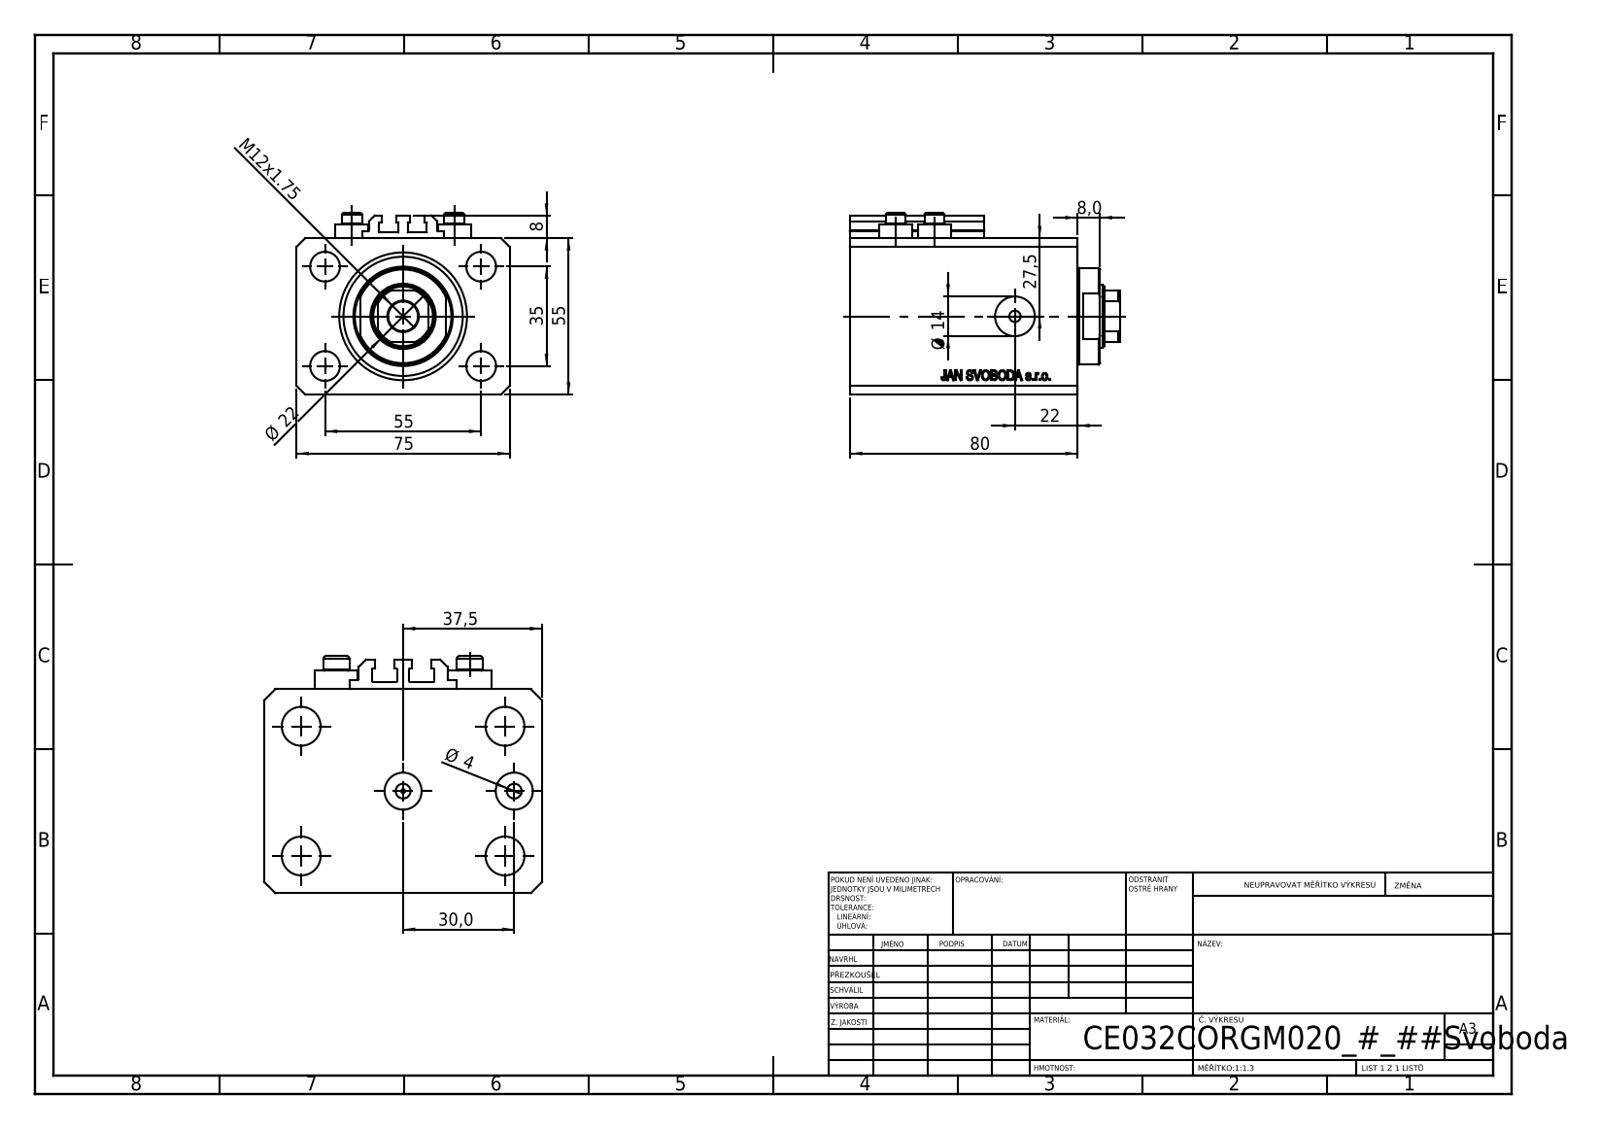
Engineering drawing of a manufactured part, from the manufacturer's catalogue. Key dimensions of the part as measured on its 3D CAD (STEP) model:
Part name (STEP PRODUCT): V250CE_C_VCP; V250CE_C_Body; ALLEN BOLT V250CE; V250CE_VC_C
STEP written by: SolidWorks 2019 (CONFIG_CONTROL_DESIGN)
Units: millimetres
Bodies: 8 solids, 1042 faces (504 planar, 92 cylindrical, 446 other)
Overall size (bounding box): 95 × 75 × 64
Volume: 304 608 mm³ · Surface area: 71 883 mm²
Round holes (diameter × count): ⌀4 ×8, ⌀10.5 ×5, ⌀10 ×2, ⌀14 ×2, ⌀1.25 ×1, ⌀22 ×1, ⌀32 ×1, ⌀45 ×1
Round bosses / shafts (diameter × count): ⌀11.6 ×4, ⌀7 ×4, ⌀34 ×1
Partial cylindrical surfaces — rounded edges, fillets, slot ends (radius × count): R0.2 ×10, R10.5 ×1
Main face-to-face distances: 55, 75, 80, 15, 65, 9.9, 55.1, 70.1, 3, 8
Hole centre spacings: 32.6, 36, 13.6, 17.68, 35, 38.48, 55, 60.1
